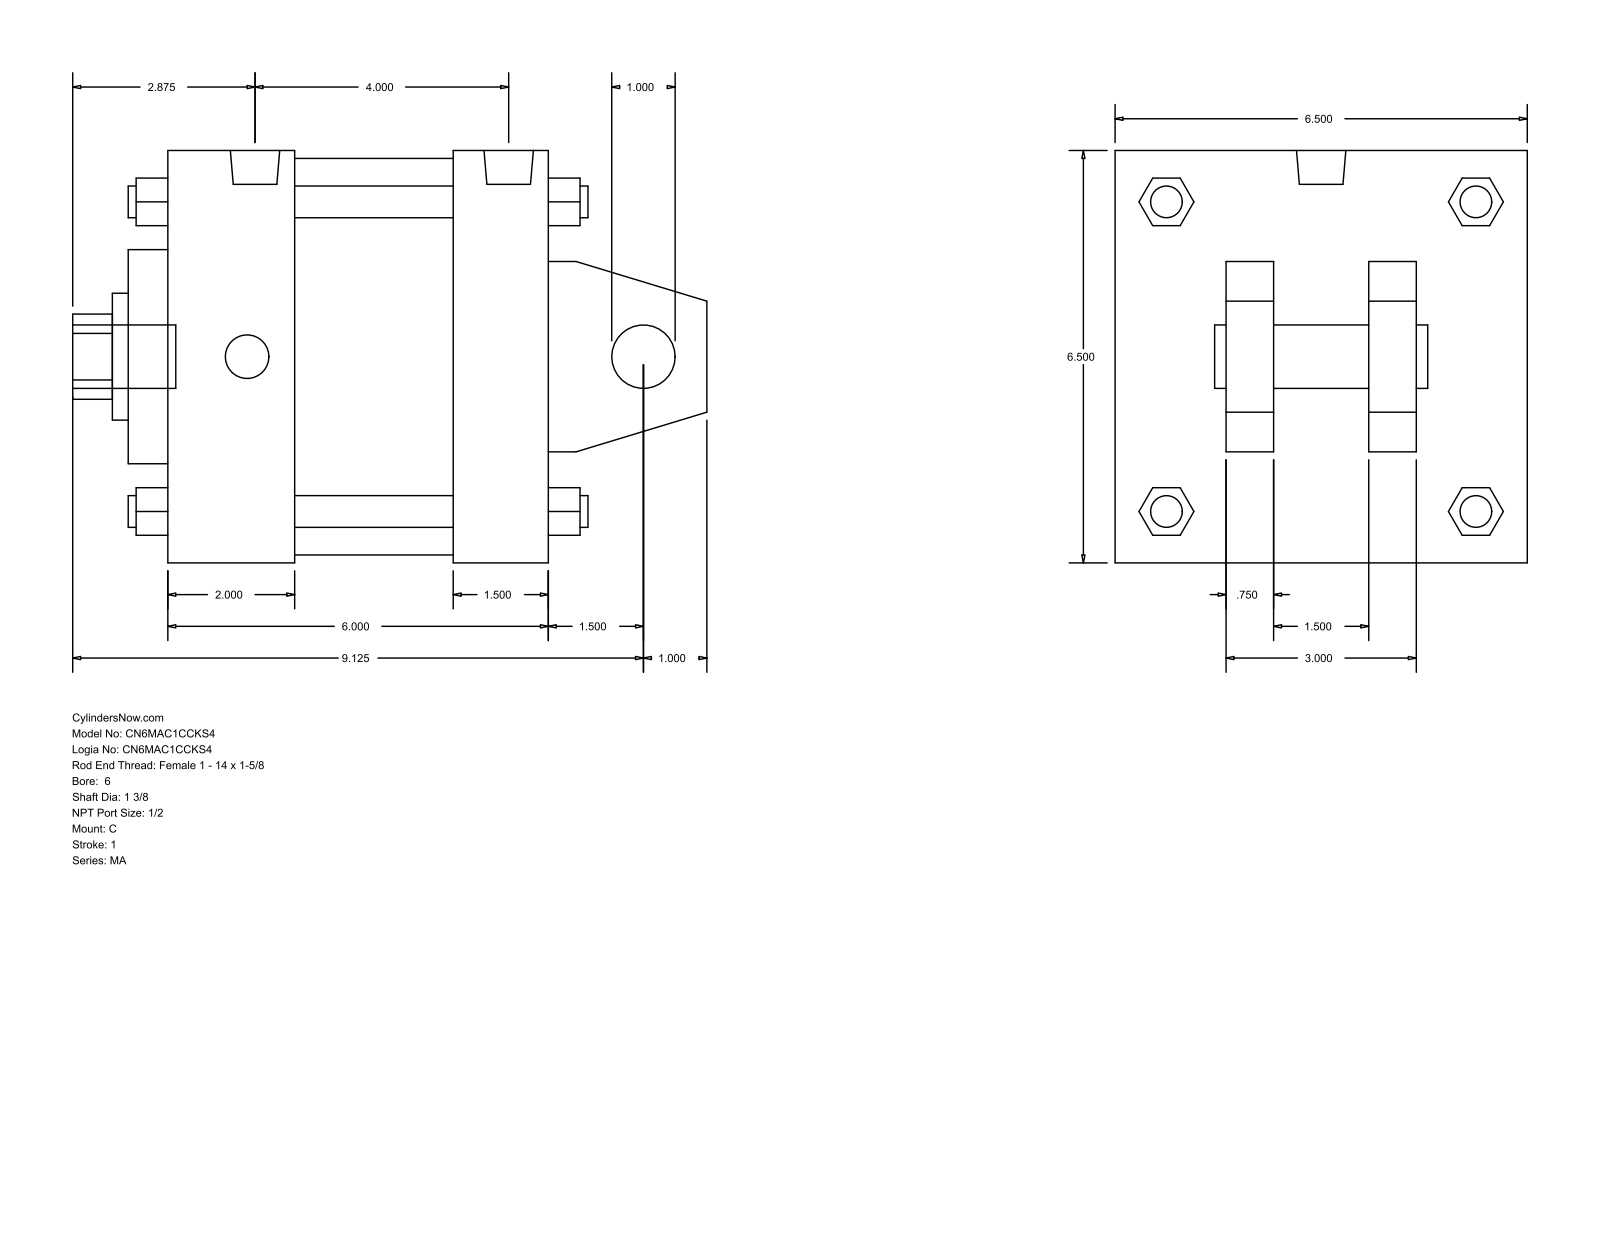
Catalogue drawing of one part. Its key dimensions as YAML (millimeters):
part_name: "MA_C__0600_1.375"
step_written_by: "GSSL Pune (CONFIG_CONTROL_DESIGN)"
units: millimeters
bodies: {solids: 0, faces: 141, planar: 109, cylindrical: 32, other: 0}
overall_size: [254, 165.1, 165.1]
round_holes:
  - {diameter: 25.4, count: 1}
  - {diameter: 34.92, count: 1}
  - {diameter: 50.8, count: 1}
  - {diameter: 85.72, count: 1}
  - {diameter: 158.75, count: 1}
round_bosses_or_shafts:
  - {diameter: 17.46, count: 4}
  - {diameter: 12.7, count: 4}
  - {diameter: 19.77, count: 2}
  - {diameter: 25.4, count: 1}
partial_cylinders:
  - {radius: 17.06, count: 1}
face_to_face_distances: [165.1, 152.4, 63.5, 101.6, 38.1, 19.05, 50.8, 44.45, 120.65, 114.3]
